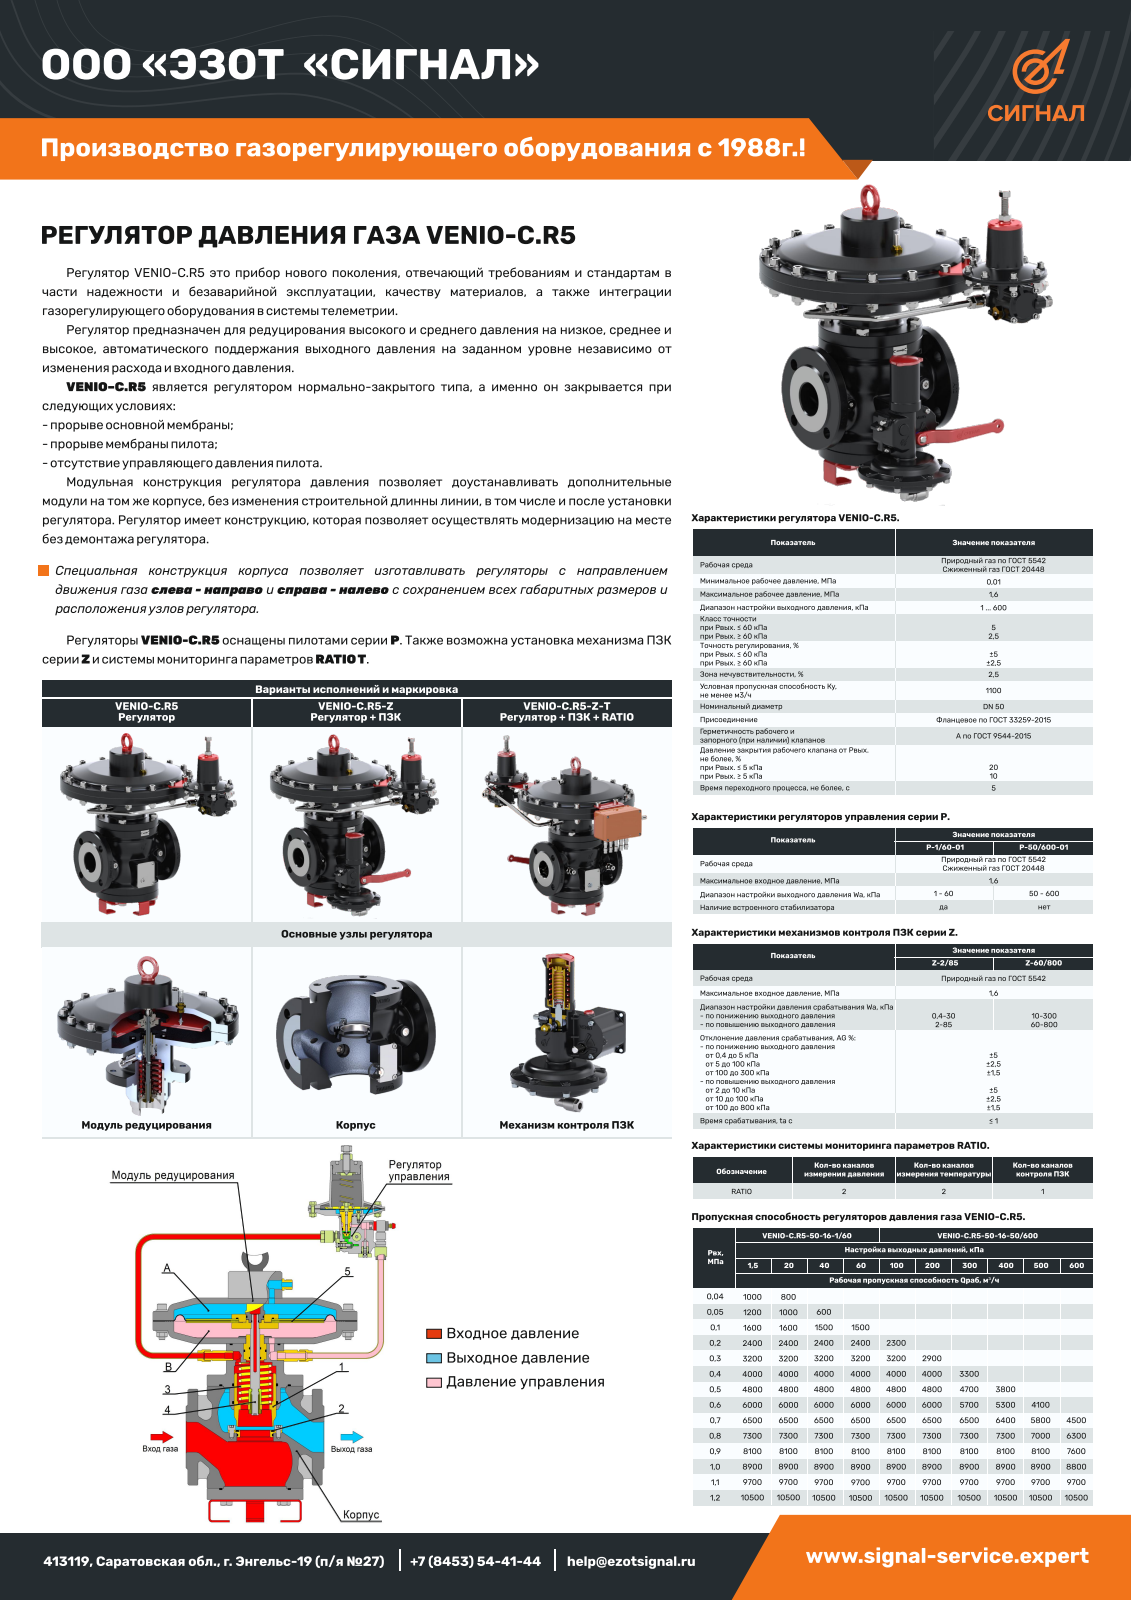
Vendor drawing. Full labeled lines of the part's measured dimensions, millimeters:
Part name (STEP PRODUCT): VENIO-C.R5
STEP written by: SolidWorks 2018 (CONFIG_CONTROL_DESIGN)
Units: millimetres
Bodies: 0 solids, 12293 faces (2837 planar, 3934 cylindrical, 5522 other)
Overall size (bounding box): 489.37 × 468.61 × 340
Round holes (diameter × count): ⌀10.5 ×18, ⌀8.38 ×16, ⌀11 ×16, ⌀6.5 ×15, ⌀4.2 ×14, ⌀8 ×14, ⌀5 ×12, ⌀9 ×11, ⌀6 ×9, ⌀12.5 ×9, ⌀3 ×8, ⌀6.4 ×8
Round bosses / shafts (diameter × count): ⌀10 ×28, ⌀20 ×25, ⌀16 ×16, ⌀12 ×14, ⌀13 ×12, ⌀5 ×12, ⌀8.5 ×10, ⌀6 ×10
Partial cylindrical surfaces — rounded edges, fillets, slot ends (radius × count): R0.5 ×484, R0.2 ×371, R1 ×339, R2 ×65, R0.1 ×52, R5 ×34, R3 ×32, R11.3 ×30
Main face-to-face distances: 1, 17, 22, 12, 44.7, 29, 3, 15.7, 27.7, 10
Hole centre spacings: 119.99, 140.13, 155.18, 158, 182.57, 191.65, 223.44, 291.94
